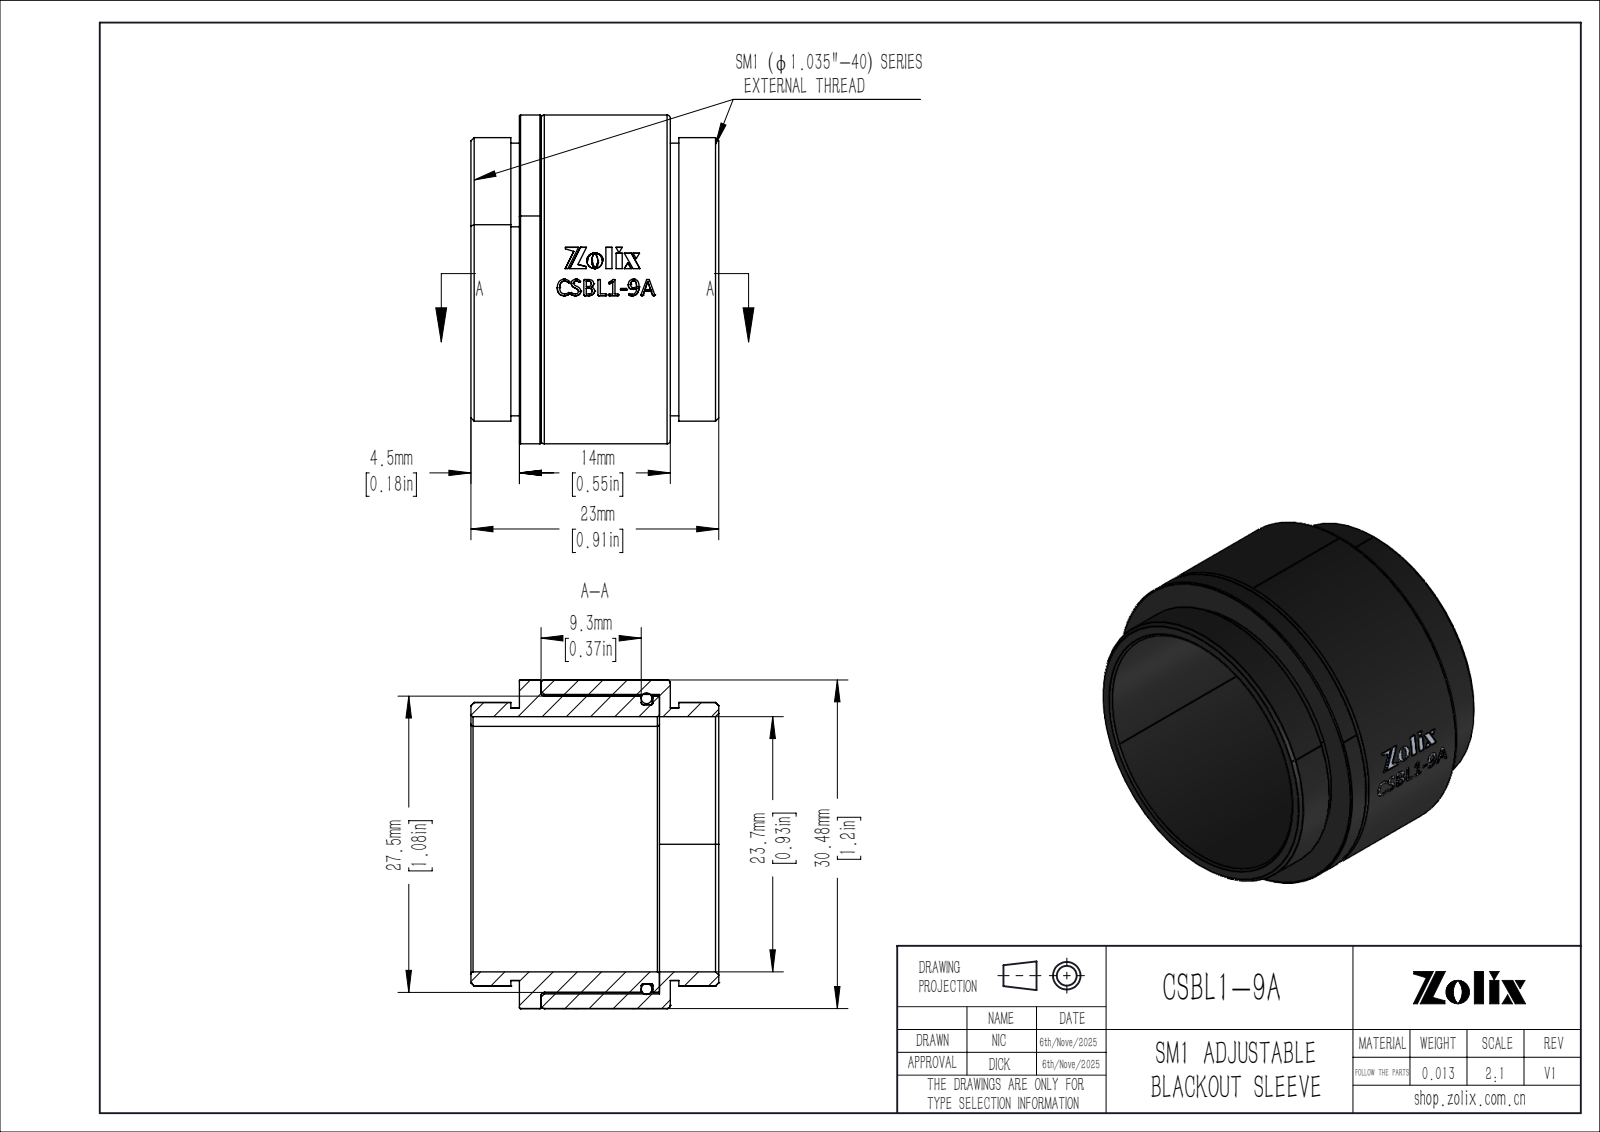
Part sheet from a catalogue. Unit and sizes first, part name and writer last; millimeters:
Units: millimetres
Overall size (bounding box): 30.5 × 30.5 × 23
Round holes (diameter × count): ⌀23.7 ×1, ⌀27.8 ×1
Round bosses / shafts (diameter × count): ⌀30.5 ×1, ⌀27.5 ×1, ⌀26.3 ×1, ⌀25.9 ×1, ⌀25.3 ×1
Partial cylindrical surfaces — rounded edges, fillets, slot ends (radius × count): R15.23 ×1
Main face-to-face distances: 13, 1, 14, 11, 12, 2, 4.5, 18.5, 3.7, 19.3
Volume: 4 743 mm³ · Surface area: 7 288 mm²
Bodies: 3 solids, 352 faces (56 planar, 46 cylindrical, 250 other)
Part name (STEP PRODUCT): CSBL1-9A
STEP written by: SolidWorks 2020 (CONFIG_CONTROL_DESIGN)
